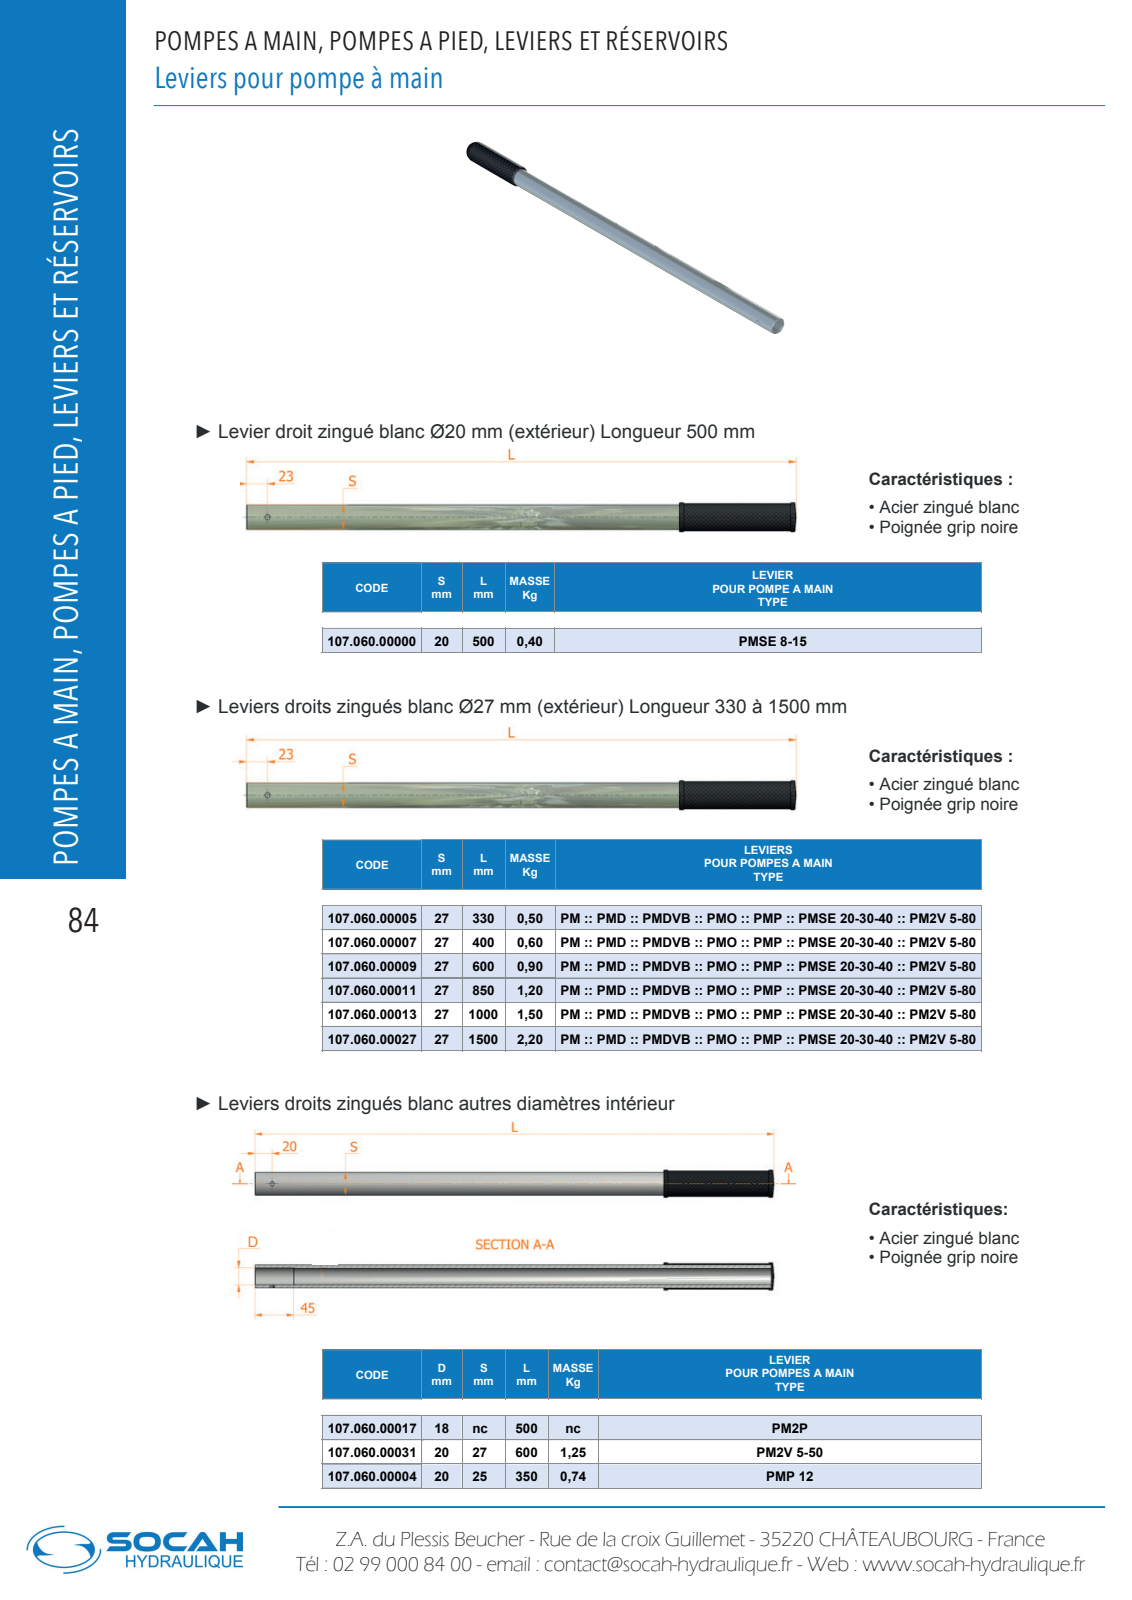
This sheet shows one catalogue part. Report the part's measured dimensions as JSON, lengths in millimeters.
{"part_name": "6077.0034.10.50 Derivazione 2", "step_written_by": "Autodesk Inventor 2013 (AUTOMOTIVE_DESIGN)", "units": "millimeters", "bodies": {"solids": 13, "faces": 1317, "planar": 591, "cylindrical": 256, "other": 470}, "overall_size": [282.13, 194.44, 117], "volume_mm3": 309374, "surface_area_mm2": 147817, "round_holes": [[9, 4], [8, 2], [17.5, 2], [18.63, 2], [19.5, 2], [4, 1], [10, 1], [13.47, 1], [21, 1], [25, 1], [28, 1], [28.5, 1]], "round_bosses_or_shafts": [[8, 4], [11.05, 3], [22.5, 2], [20, 2], [16, 2], [10, 2], [47, 1], [38, 1]], "partial_cylinders_radius": [[0.2, 24], [2, 21], [1, 20], [0.1, 16], [5, 10], [0.36, 6], [0.53, 6], [2.5, 6]], "face_to_face_distances": [4, 20, 16, 87, 17.5, 24, 10, 7.5, 12, 8], "hole_center_spacings": [30.15, 60, 87, 89.2, 105.68, 26.39, 106.81]}
